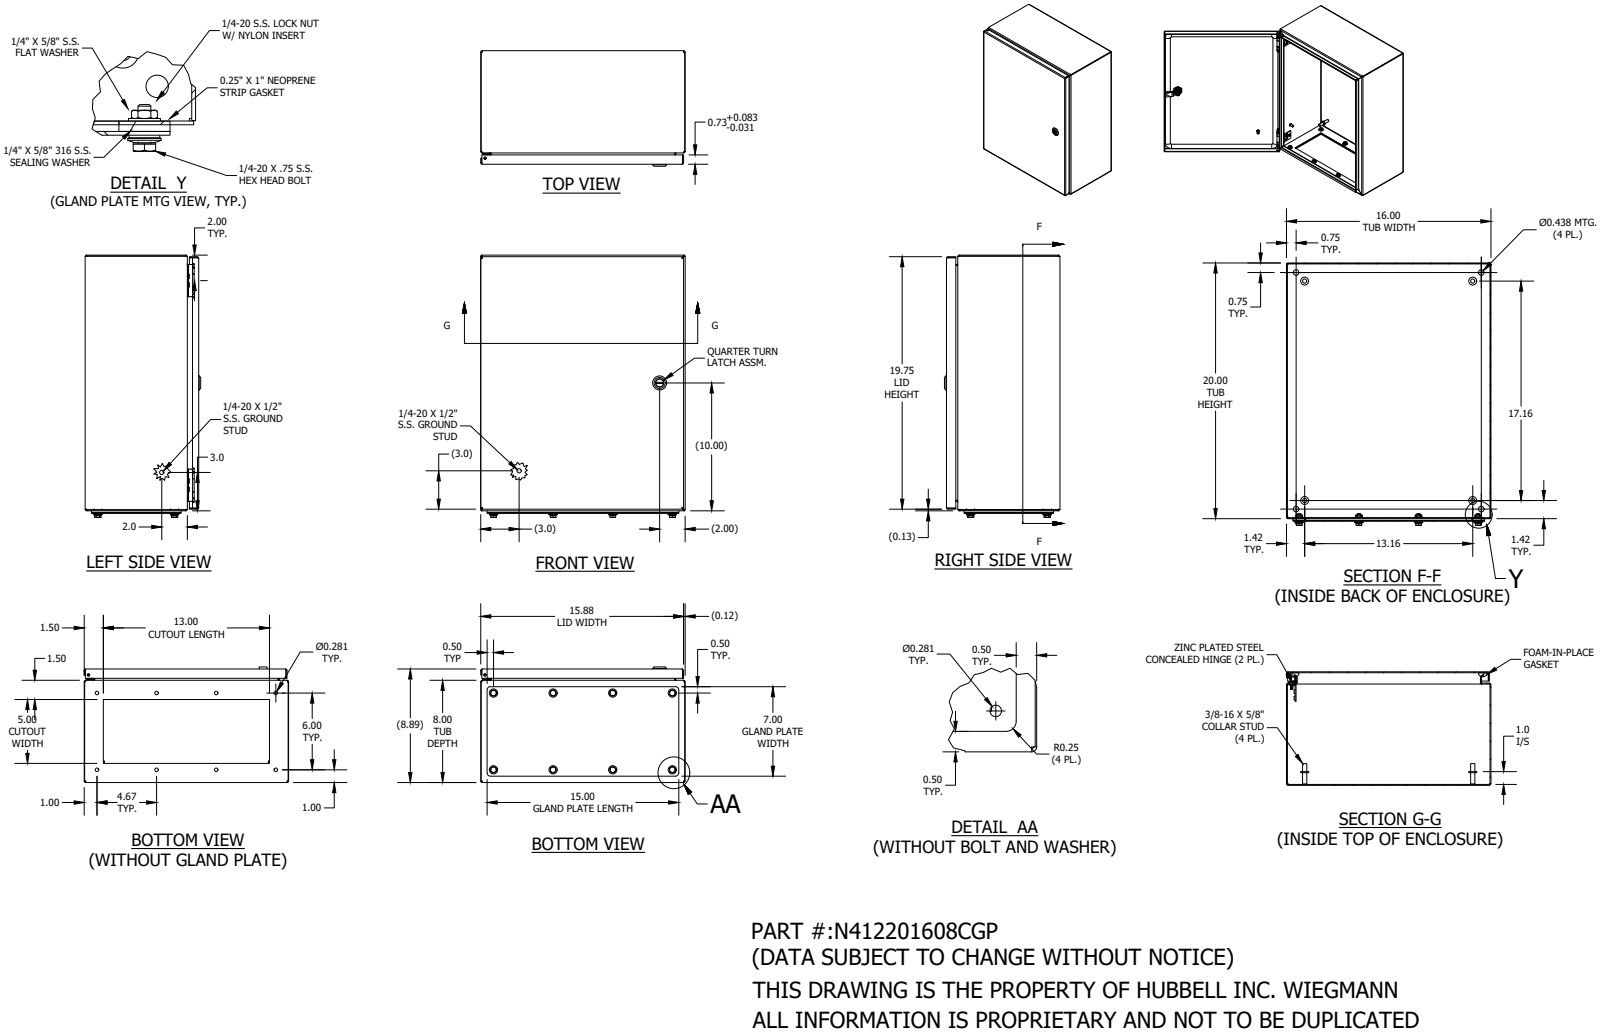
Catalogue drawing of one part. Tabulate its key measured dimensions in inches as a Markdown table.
| quantity | value |
| --- | --- |
| part name | N412201608CGP |
| STEP written by | SolidWorks 2019 (AUTOMOTIVE_DESIGN) |
| units | inches |
| bodies | 71 solids, 2035 faces (794 planar, 624 cylindrical, 617 other) |
| overall size | 20.519 × 16 × 9.044 |
| volume | 124.3 in³ |
| surface area | 3 066 in² |
| round holes (diameter × count) | 0.16 × 8, 0.211 × 8, 0.281 × 8, 0.29 × 8, 0.35 × 6, 0.188 × 5, 0.093 × 4, 0.167 × 4, 0.235 × 4, 0.235 × 4, 0.275 × 4, 0.275 × 4 |
| round bosses / shafts (diameter × count) | 0.25 × 18, 0.65 × 8, 0.6 × 8, 0.438 × 8, 0.625 × 7, 0.625 × 5, 0.36 × 4, 0.33 × 4 |
| partial cylindrical surfaces (radius × count) | 0.012 × 30, 0.05 × 26, 0.047 × 20, 0.121 × 20, 0.02 × 13, 0.125 × 8, 0.13 × 8, 0.157 × 5 |
| main face-to-face distances | 0.074, 8.812, 0.074, 8.738, 15.926, 8.886, 20.13, 15.852, 16, 20.056 |
| hole center spacings | 7.601, 6, 4.667, 16.004, 0.658, 0.66, 4.667, 9.333 |
